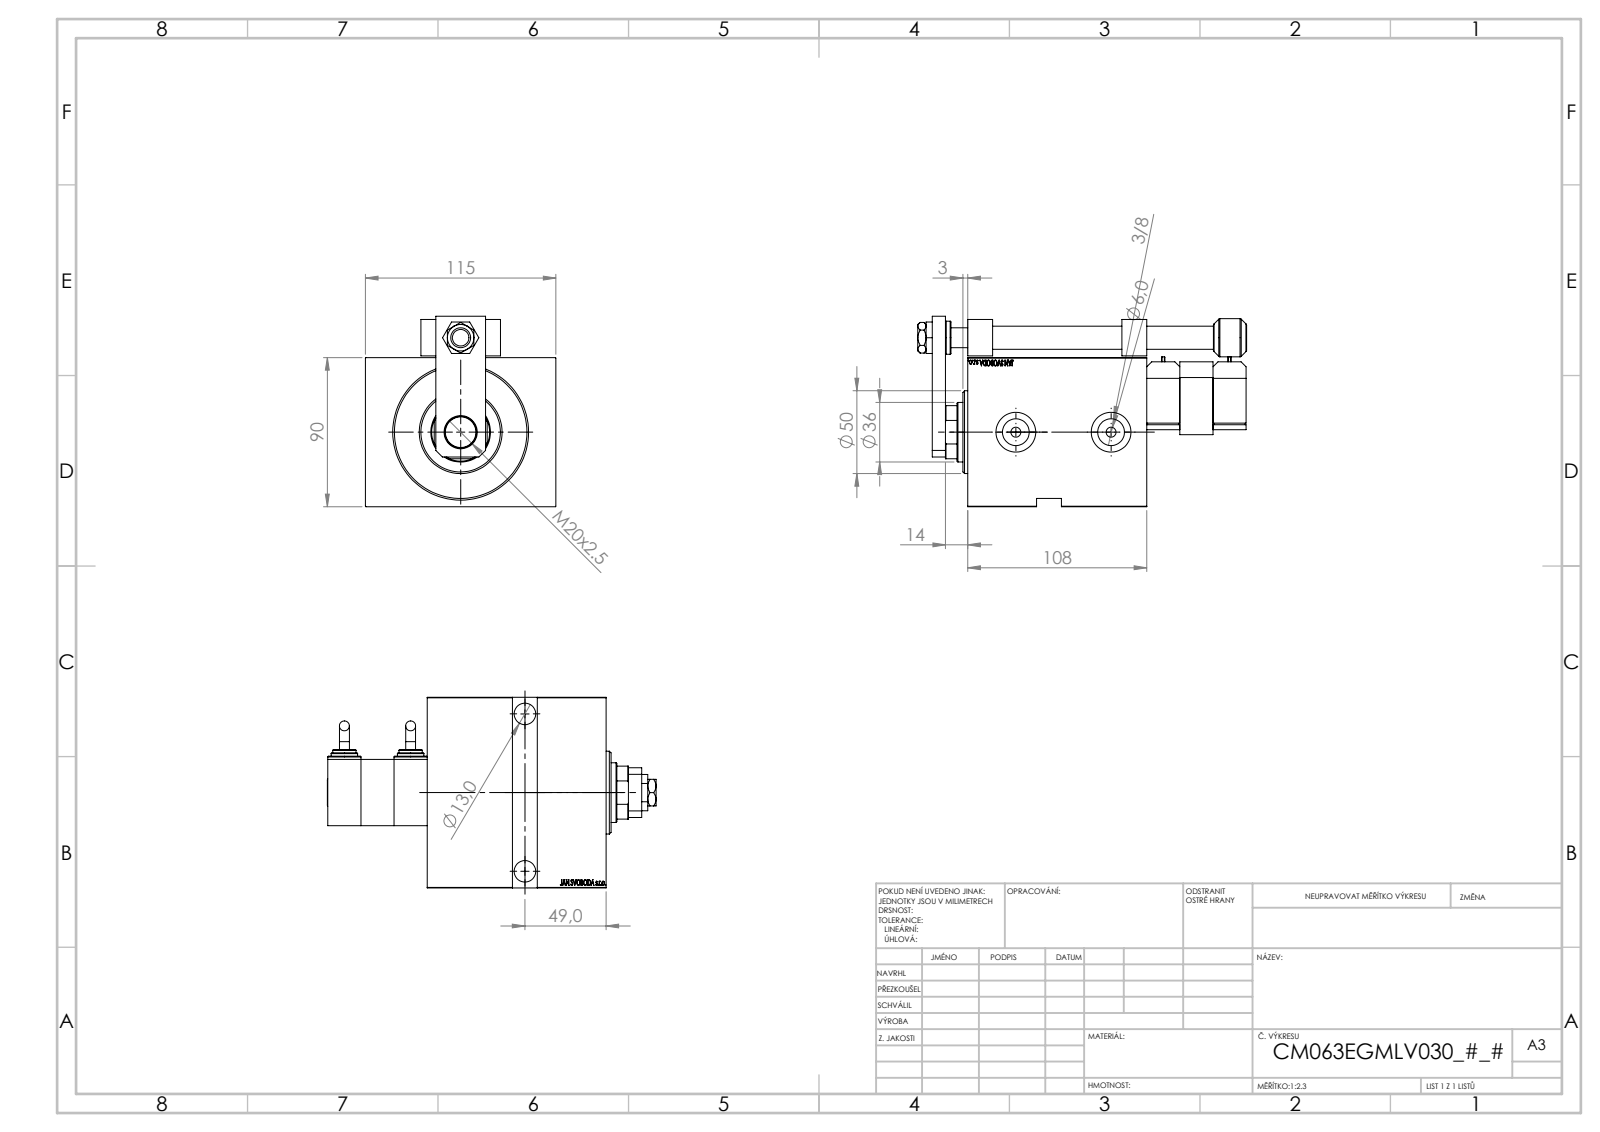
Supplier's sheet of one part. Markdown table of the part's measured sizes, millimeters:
| quantity | value |
| --- | --- |
| part name | V450CM_E_VCP; NUT_D16; ZARAZKA_P; SWITCH P (+7 more) |
| STEP written by | SolidWorks 2019 (CONFIG_CONTROL_DESIGN) |
| units | millimeters |
| bodies | 14 solids, 1076 faces (523 planar, 104 cylindrical, 449 other) |
| overall size | 198.5 × 115 × 115 |
| volume | 1 144 000 mm³ |
| surface area | 177 982 mm² |
| round holes (diameter × count) | 4 × 4, 8 × 4, 13 × 3, 6 × 2, 16.17 × 2, 19 × 2, 24 × 2, 12 × 1, 14 × 1, 18.5 × 1, 20 × 1, 28 × 1 |
| round bosses / shafts (diameter × count) | 20 × 3, 16 × 2, 14 × 2, 6 × 2, 50 × 1, 23 × 1 |
| partial cylindrical surfaces (radius × count) | 3 × 1, 13.5 × 1 |
| main face-to-face distances | 90, 108, 115, 20, 19, 5, 89, 40, 39, 18.5 |
| hole center spacings | 20, 55.93, 63.71, 70.91, 77.19, 93, 95.13, 57 |
